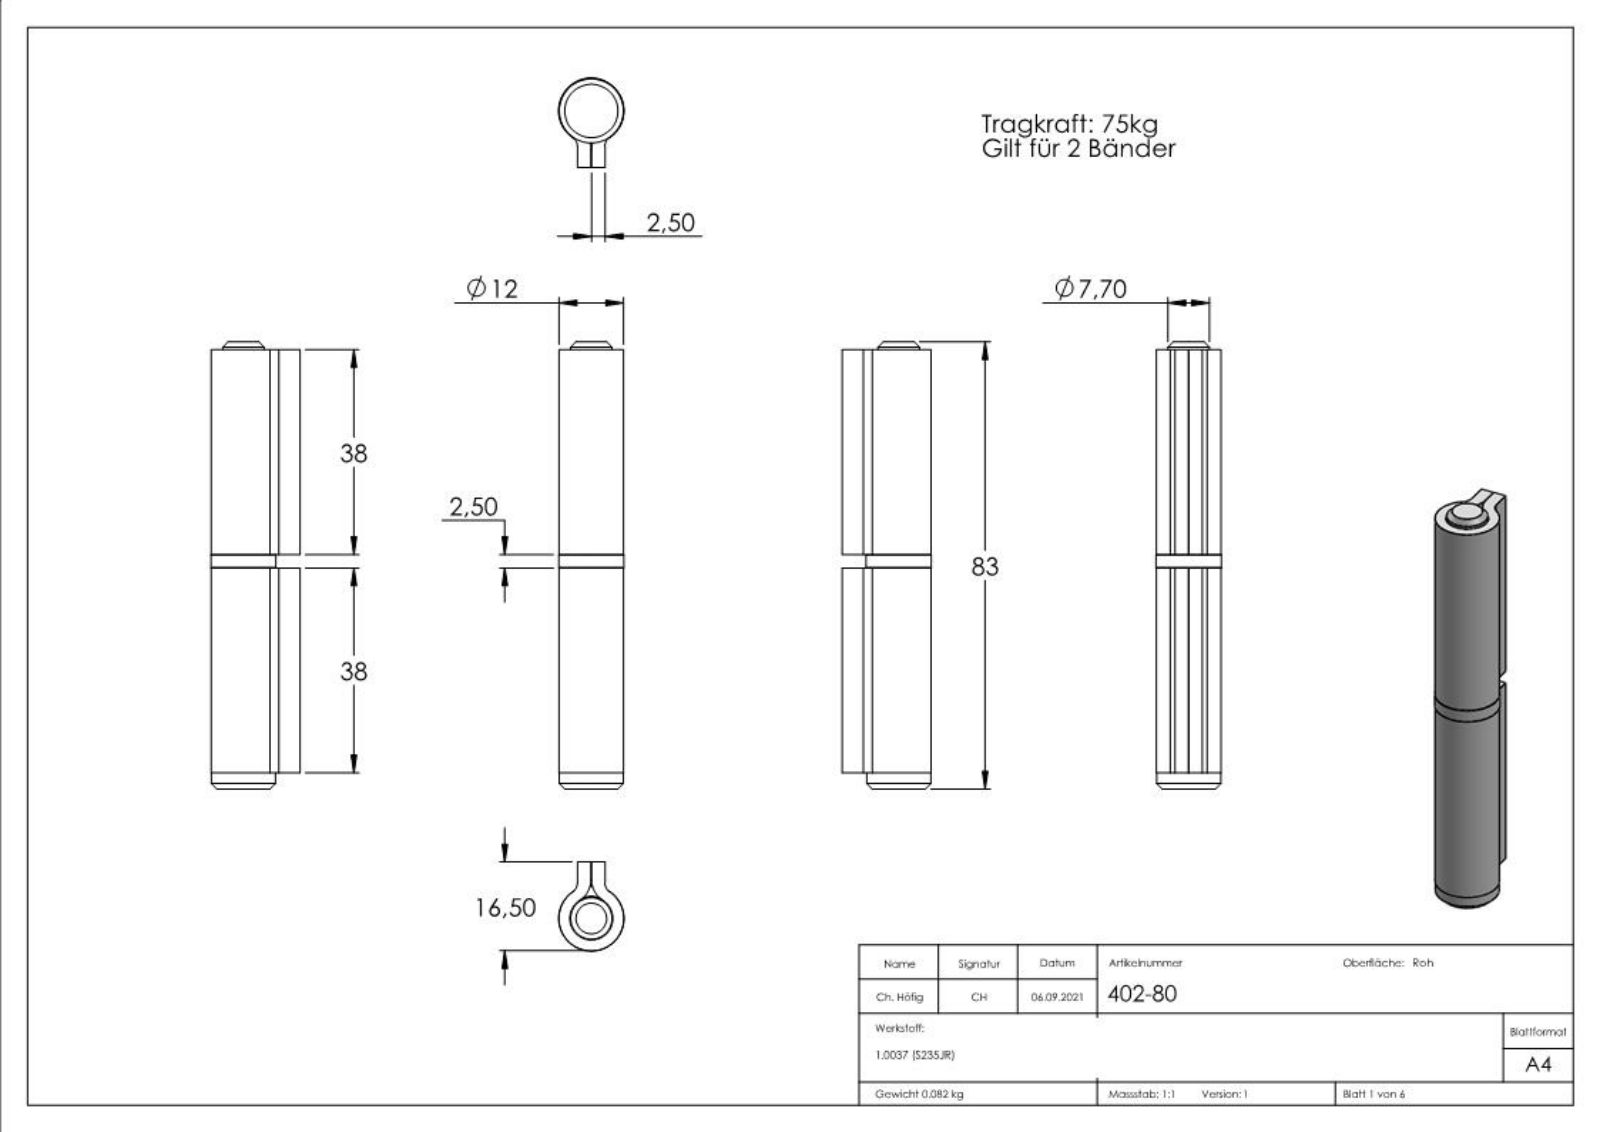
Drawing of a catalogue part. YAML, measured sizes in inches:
part_name: "402-xx Teil4; 402-xx Teil2_402-80 Teil2; 402-xx Teil2; 402-80 (+5 more)"
step_written_by: "SolidWorks 2018 (CONFIG_CONTROL_DESIGN)"
units: inches
bodies: {solids: 4, faces: 317, planar: 142, cylindrical: 40, other: 135}
overall_size: [3.268, 0.652, 0.476]
volume: 0.643
surface_area: 14.26
round_holes:
  - {diameter: 0.315, count: 1}
round_bosses_or_shafts:
  - {diameter: 0.476, count: 1}
  - {diameter: 0.472, count: 1}
  - {diameter: 0.469, count: 1}
  - {diameter: 0.303, count: 1}
partial_cylinders:
  - {radius: 0.079, count: 2}
  - {radius: 0.177, count: 2}
  - {radius: 0.161, count: 1}
face_to_face_distances: [0.098, 0.102, 0.201, 1.594, 1.496, 3.091, 0.118, 1.614, 1.713, 3.209]
